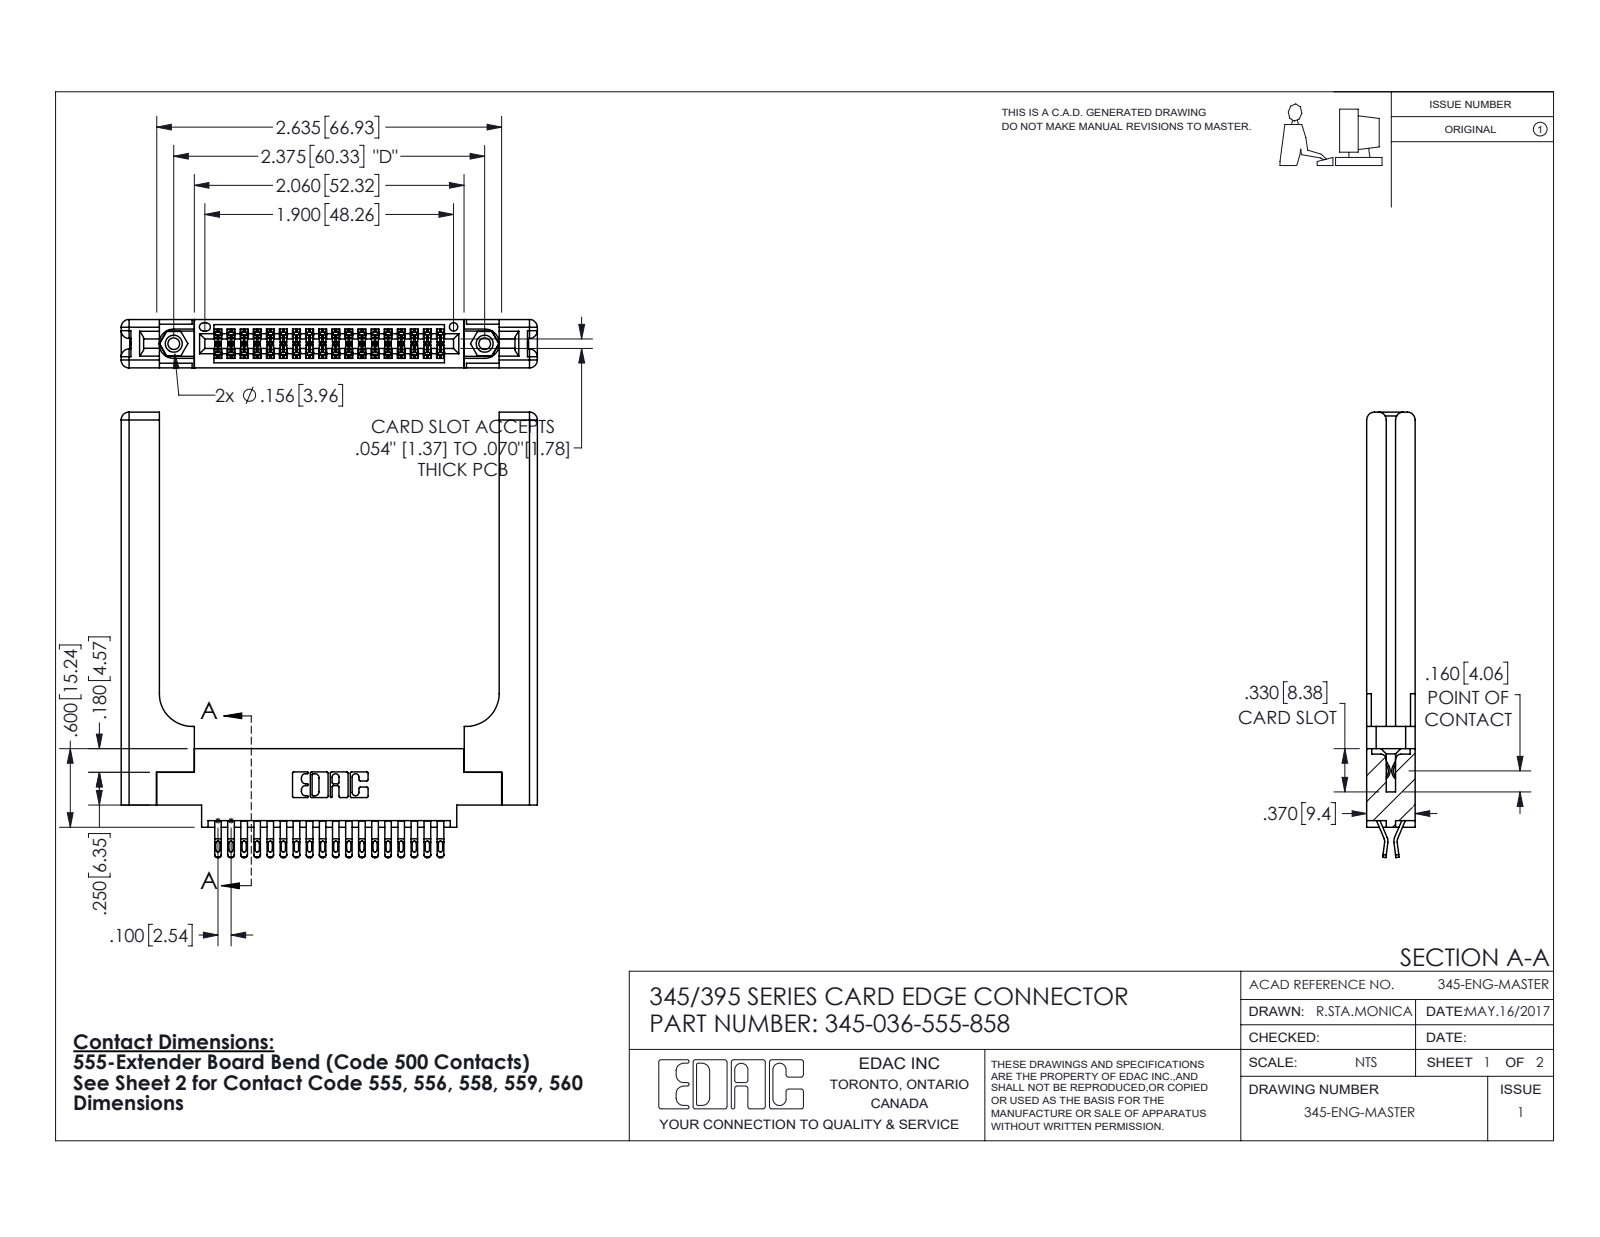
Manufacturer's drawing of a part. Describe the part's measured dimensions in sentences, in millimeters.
The part is named "345-036-555-858; 345 Part_0.170 Offset - 0.156 Dia-TH; 345-220-058_345-220-058; 345-250-001_345-250-001-102 (+1 more)". Its 3-D file was written by "SolidWorks 2016 (CONFIG_CONTROL_DESIGN)". It is 41 solids with 2402 faces: 1348 planar, 994 cylindrical and 60 other. Overall it measures 86.4 by 80.7 by 9.4 millimeters. Its volume is 16 100 cubic millimeters and its surface area 16 350 square millimeters. Round holes: 2 of diameter 2.3, 2 of diameter 3.2, 2 of diameter 4, 1 of diameter 1.6. Round bosses or shafts: 2 of diameter 3.9. Partial cylindrical surfaces (rounded edges, fillets, slot ends): 90 of radius 0.4, 72 of radius 0.5, 54 of radius 0.2, 22 of radius 0.3, 16 of radius 1.5, 6 of radius 0.2, 6 of radius 0.8, 3 of radius 0.7. The main face-to-face distances are 9.4, 1.8, 7.6, 3.8, 3.8, 2, 5.6, 0.6, 5.7, 3.1. The hole center spacings are 6.9, 54.4, 60.3.
